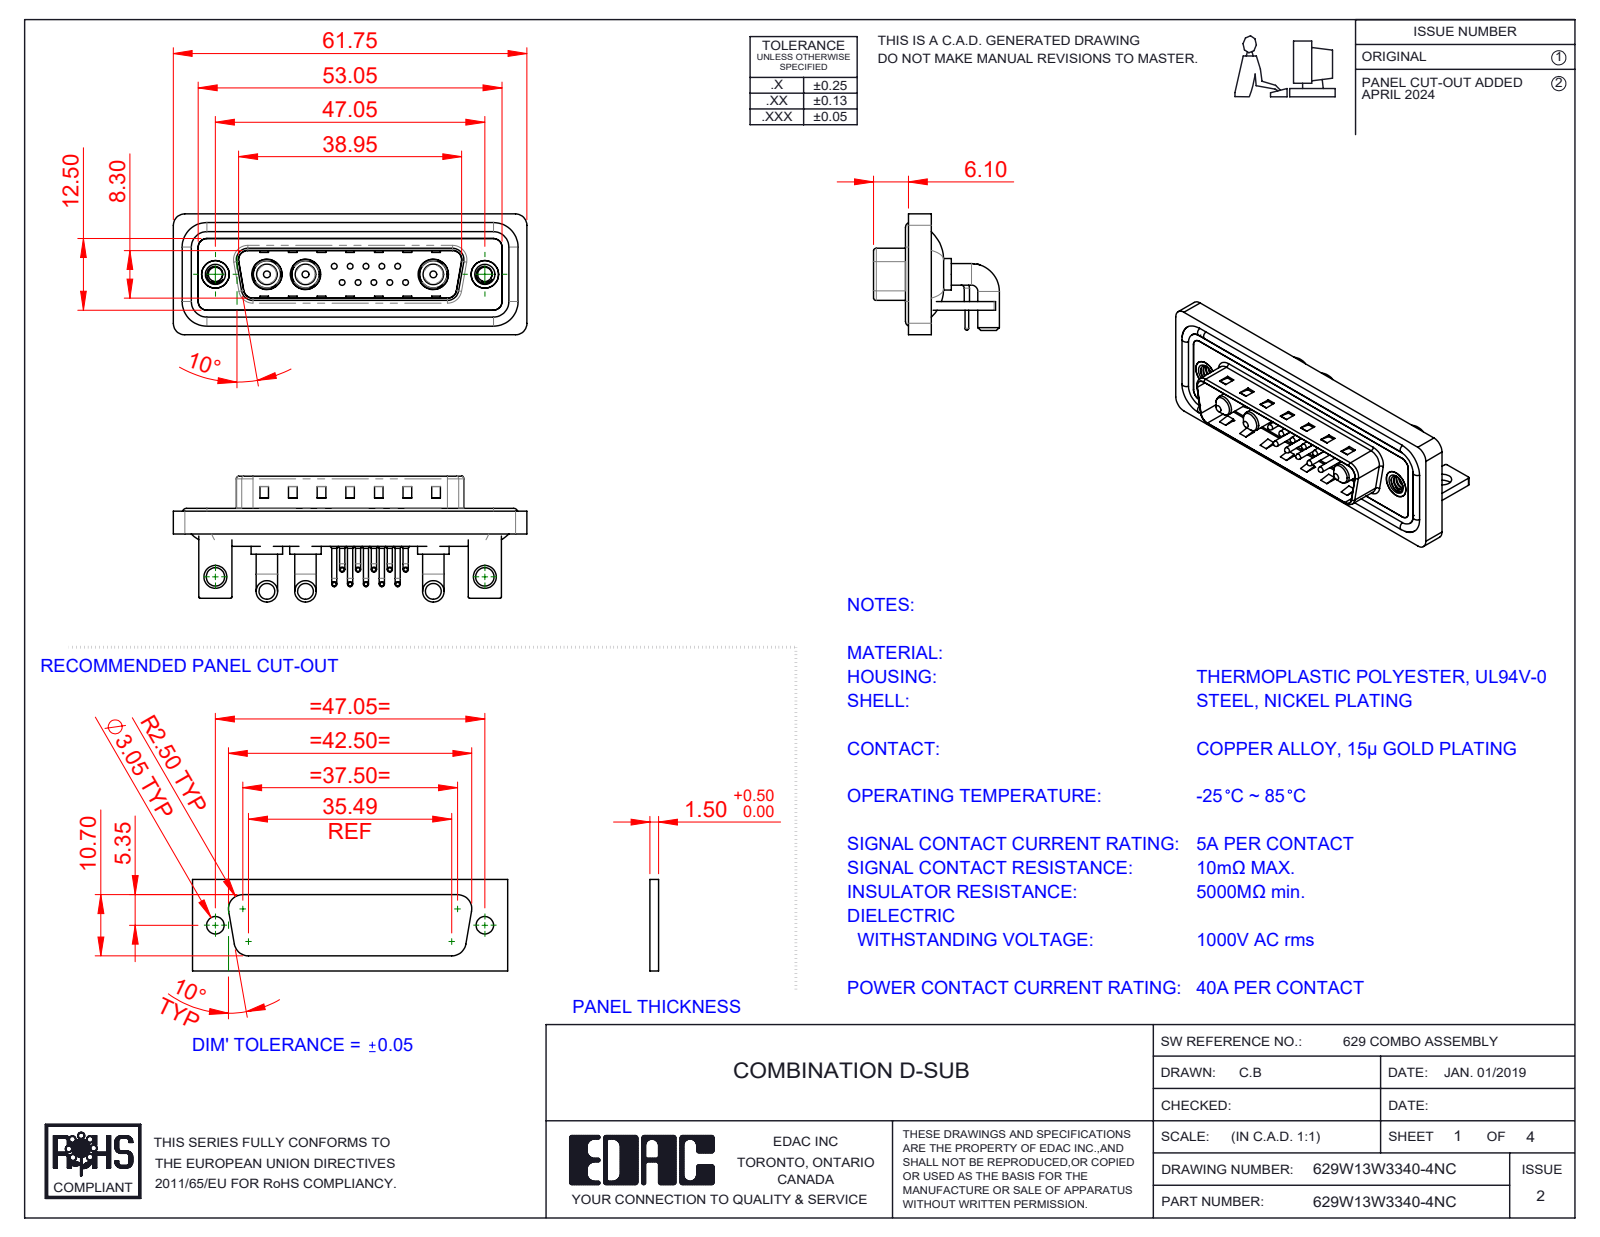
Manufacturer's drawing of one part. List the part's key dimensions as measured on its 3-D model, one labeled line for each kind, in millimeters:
Part name (STEP PRODUCT): 629Combo Waterproof Housing_25 Contacts; 629Combo Contact Row 1; 629Combo Housing_13W3; 629W13W3340-4NC (+6 more)
STEP written by: SolidWorks 2023 (CONFIG_CONTROL_DESIGN)
Units: millimetres
Bodies: 25 solids, 1750 faces (899 planar, 629 cylindrical, 222 other)
Overall size (bounding box): 61.75 × 21.98 × 21.1
Volume: 8 101 mm³ · Surface area: 13 216 mm²
Round holes (diameter × count): ⌀0.75 ×10, ⌀1.6 ×10, ⌀2 ×10, ⌀4.85 ×3, ⌀5.3 ×3, ⌀2.5 ×2, ⌀3.2 ×2, ⌀4 ×2, ⌀4.8 ×2, ⌀5 ×2
Round bosses / shafts (diameter × count): ⌀0.9 ×20, ⌀1.5 ×10, ⌀1 ×10, ⌀0.65 ×10, ⌀3.75 ×6, ⌀1.6 ×4, ⌀5.5 ×3, ⌀5.2 ×3
Partial cylindrical surfaces — rounded edges, fillets, slot ends (radius × count): R2 ×19, R1.5 ×18, R0.25 ×16, R1.01 ×10, R0.5 ×9, R1.6 ×8, R0.6 ×4, R0.65 ×4
Main face-to-face distances: 0.4, 0.8, 1.5, 2.9, 2.1, 1.1, 4.1, 1.6, 3.7, 4.5
Hole centre spacings: 3.16, 2.77, 5.04, 5.54, 7.49, 5.03, 8.31, 10.11
